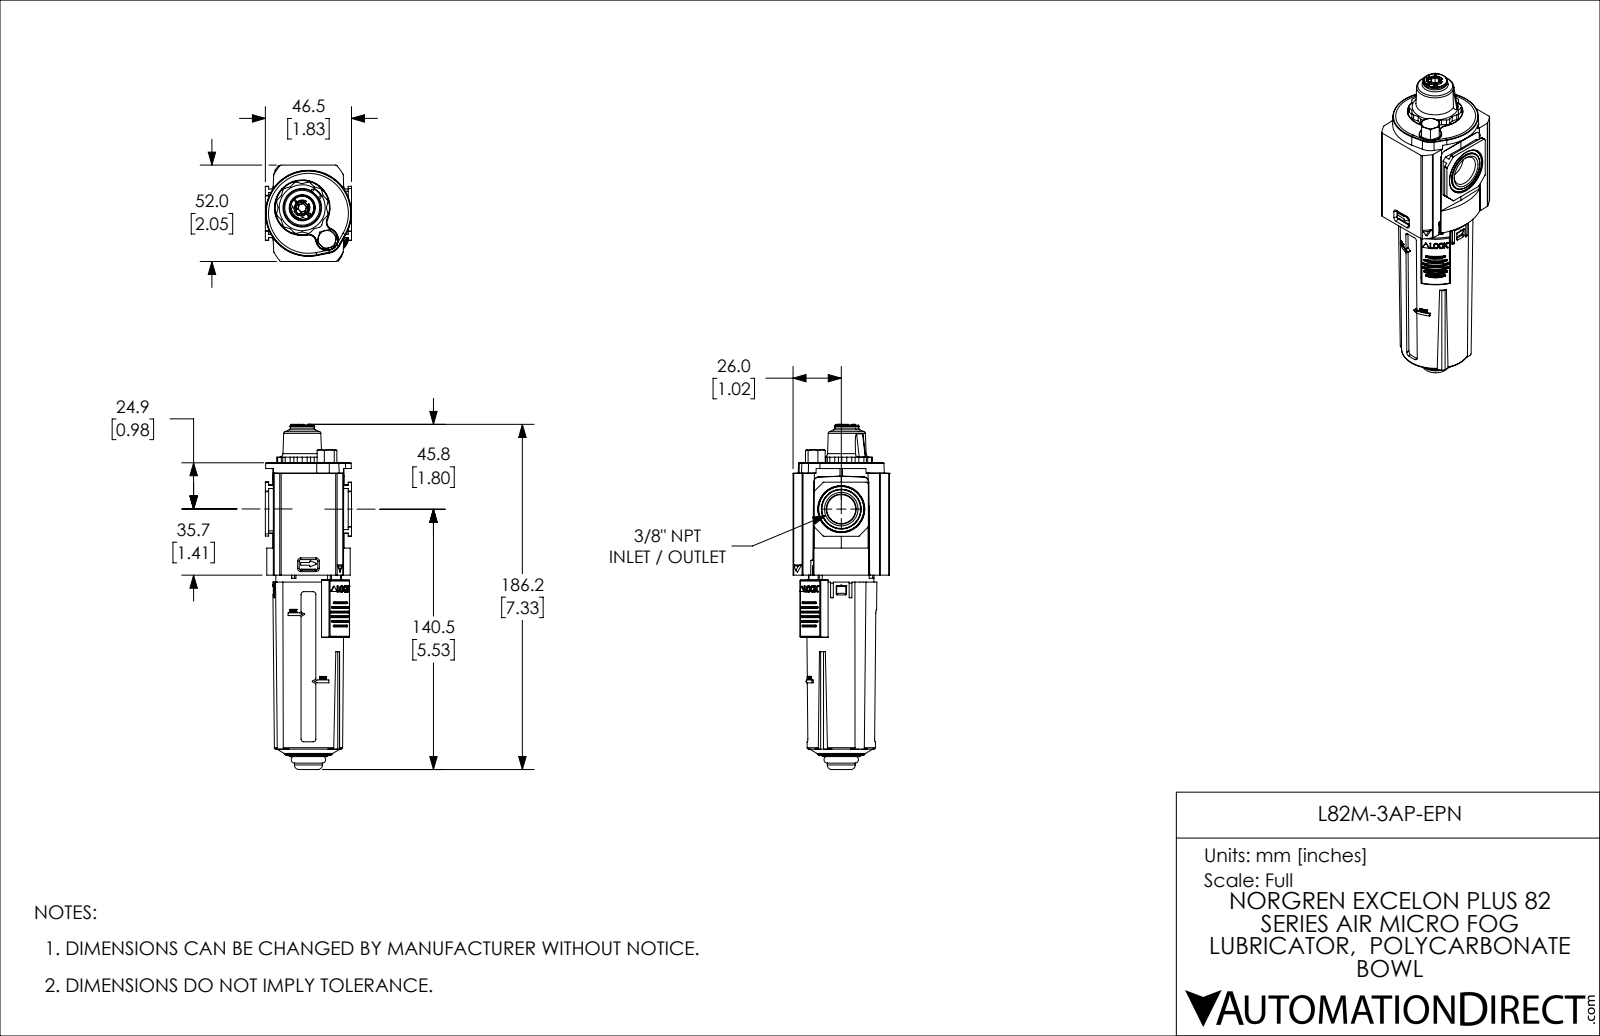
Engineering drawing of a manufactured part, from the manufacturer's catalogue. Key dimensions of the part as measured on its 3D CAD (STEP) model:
Part name (STEP PRODUCT): L82M-3AP-EPN
STEP written by: SolidWorks 2021 (CONFIG_CONTROL_DESIGN)
Units: inches
Bodies: 7 solids, 1298 faces (592 planar, 456 cylindrical, 250 other)
Overall size (bounding box): 7.331 × 2.047 × 1.831
Volume: 13.05 in³ · Surface area: 95.07 in²
Round holes (diameter × count): ⌀0.271 ×1, ⌀0.312 ×1, ⌀0.312 ×1, ⌀0.354 ×1, ⌀0.63 ×1, ⌀0.943 ×1, ⌀1.181 ×1
Round bosses / shafts (diameter × count): ⌀0.24 ×2, ⌀1.388 ×1, ⌀1.356 ×1, ⌀1.291 ×1, ⌀1.257 ×1, ⌀1.161 ×1, ⌀0.906 ×1, ⌀0.626 ×1
Partial cylindrical surfaces — rounded edges, fillets, slot ends (radius × count): R0.02 ×58, R0.039 ×30, R0.008 ×22, R0.01 ×12, R0.075 ×12, R0.012 ×11, R0.059 ×10, R0.118 ×9
Main face-to-face distances: 0.059, 1.988, 2.047, 1.929, 0.236, 1.352, 0.182, 1.475, 1.417, 1.293
Hole centre spacings: 0.177, 0.677, 0.851
